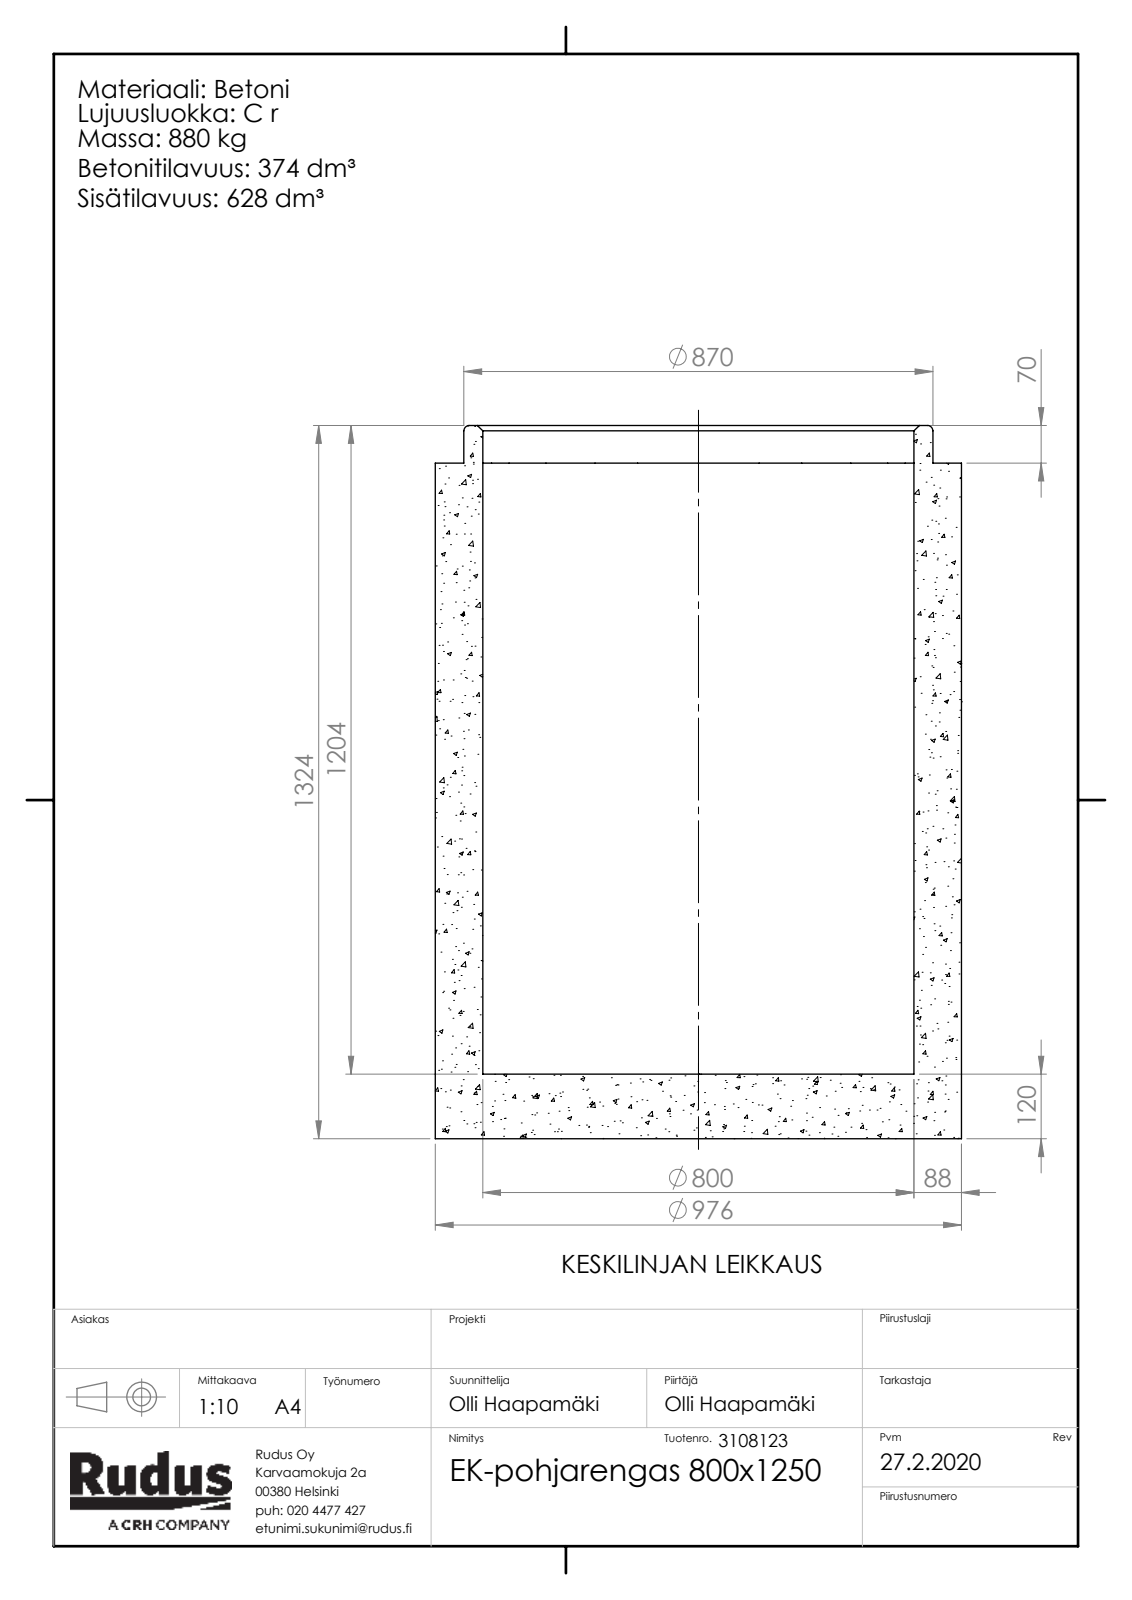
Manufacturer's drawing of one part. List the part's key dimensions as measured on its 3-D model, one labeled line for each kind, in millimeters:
Part name (STEP PRODUCT): Rudus 3108123 EK-pohjarengas 800x1250; EK-osa-kaivorunko_EK-pohjarengas
STEP written by: SolidWorks 2019 (CONFIG_CONTROL_DESIGN)
Units: millimetres
Bodies: 1 solid, 95 faces (5 planar, 6 cylindrical, 84 other)
Overall size (bounding box): 1324 × 976 × 976
Volume: 374 400 000 mm³ · Surface area: 8 537 000 mm²
Round holes (diameter × count): ⌀800 ×1
Round bosses / shafts (diameter × count): ⌀976 ×1, ⌀870 ×1
Main face-to-face distances: 120, 1254, 1134, 1324, 1204, 70, 687.01, 567.01, 566.99, 636.99
